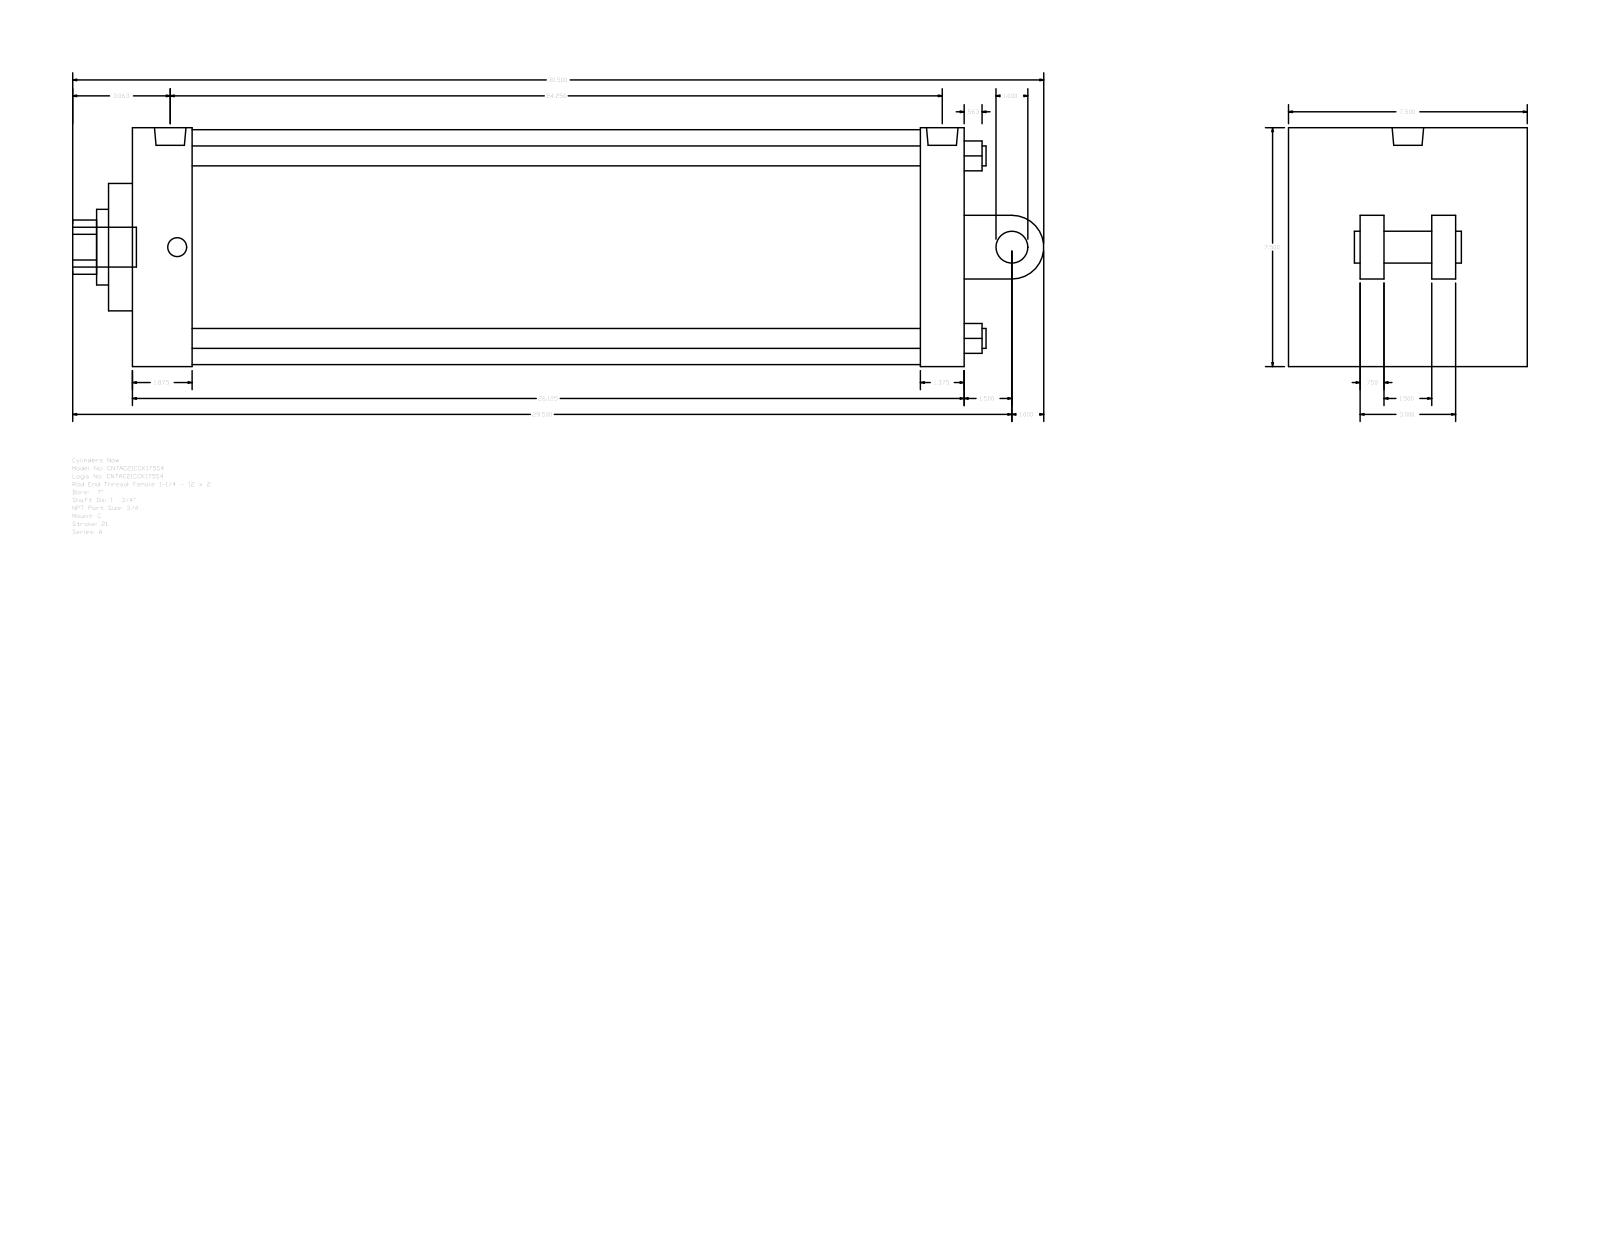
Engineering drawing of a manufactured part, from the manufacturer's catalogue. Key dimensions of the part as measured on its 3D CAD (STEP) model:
Part name (STEP PRODUCT): A_C__0700_1.75
STEP written by: GSSL Pune (CONFIG_CONTROL_DESIGN)
Units: millimetres
Bodies: 0 solids, 104 faces (75 planar, 29 cylindrical, 0 other)
Overall size (bounding box): 774.7 × 190.5 × 190.5
Round holes (diameter × count): ⌀15.88 ×4, ⌀15.08 ×2, ⌀25.12 ×1, ⌀44.45 ×1, ⌀60.33 ×1, ⌀187.32 ×1
Round bosses / shafts (diameter × count): ⌀15.08 ×2, ⌀31.75 ×1, ⌀25.4 ×1, ⌀25.12 ×1
Partial cylindrical surfaces — rounded edges, fillets, slot ends (radius × count): R21.63 ×1, R25.4 ×1
Main face-to-face distances: 190.5, 663.58, 19.05, 76.2, 57.15, 44.45, 47.63, 615.95, 628.65, 581.02
Hole centre spacings: 102.91, 145.54, 205.82, 5.56
